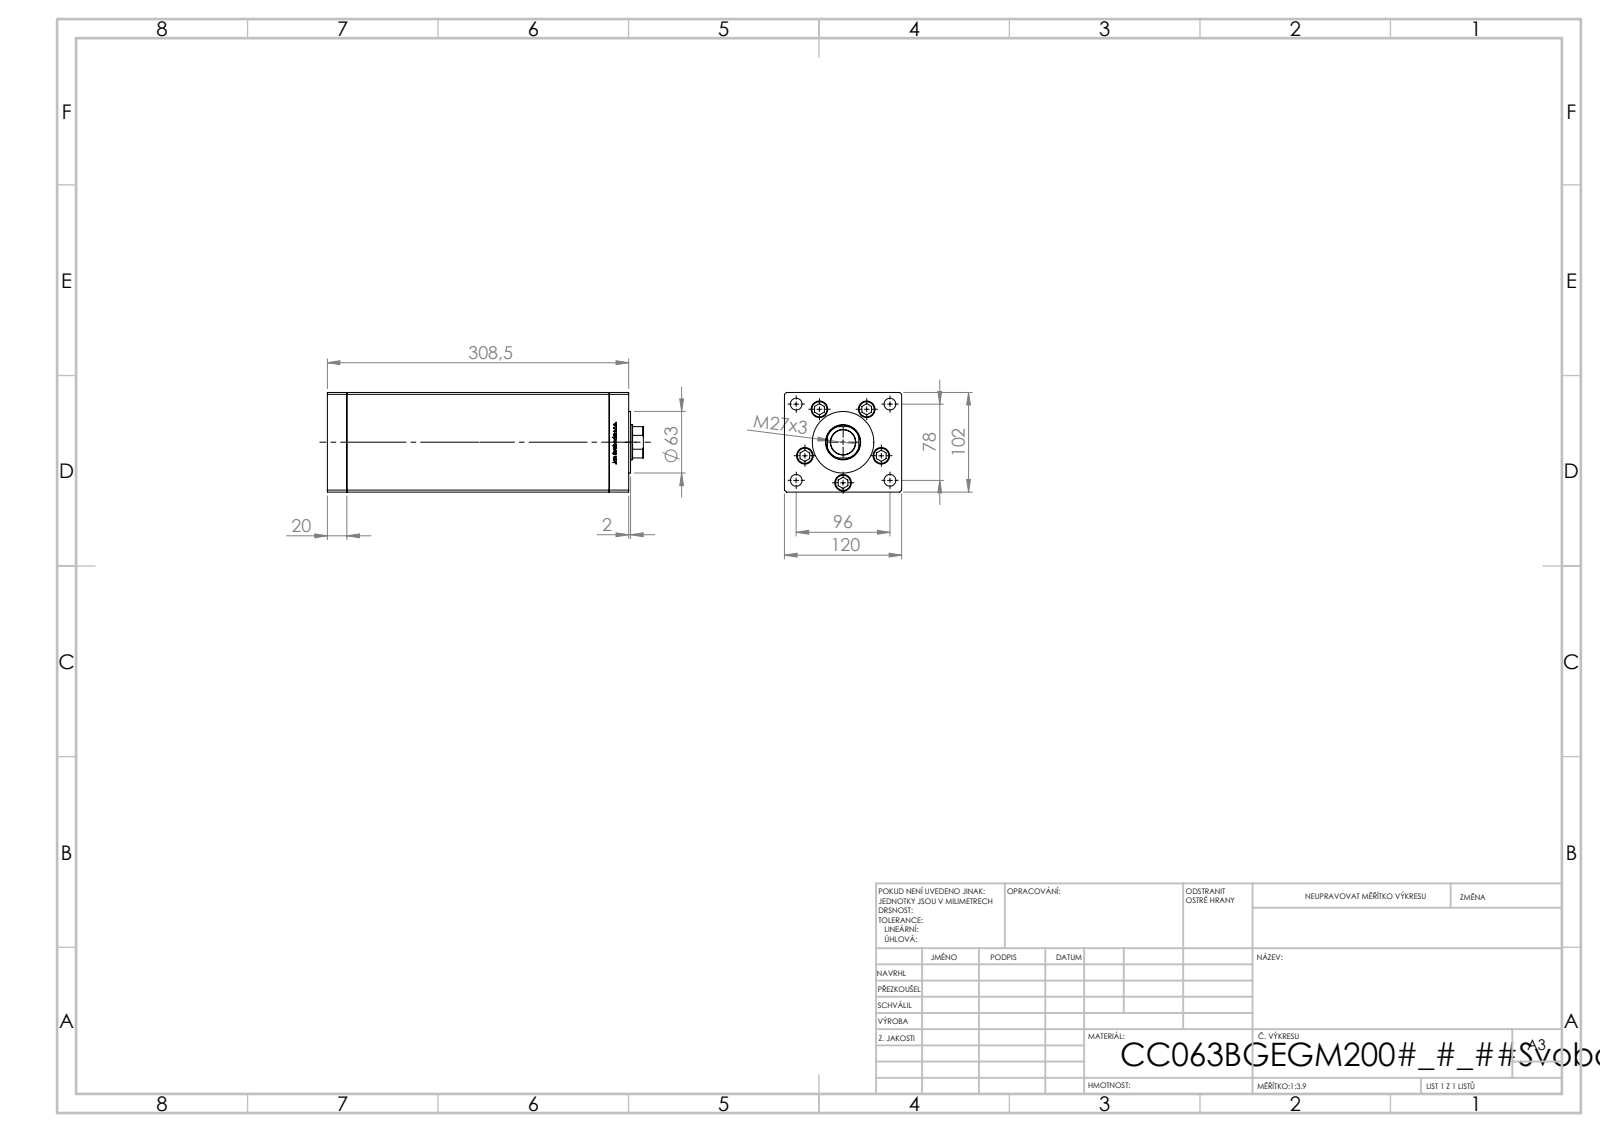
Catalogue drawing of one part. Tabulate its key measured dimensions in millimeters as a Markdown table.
| quantity | value |
| --- | --- |
| part name | V220C BACK_B; V220C_FRONT_B; V220C_B MIDDLE; ALLEN BOLT (+1 more) |
| STEP written by | SolidWorks 2019 (CONFIG_CONTROL_DESIGN) |
| units | millimeters |
| bodies | 14 solids, 1185 faces (464 planar, 147 cylindrical, 574 other) |
| overall size | 323.5 × 120 × 102 |
| volume | 3 241 000 mm³ |
| surface area | 348 914 mm² |
| round holes (diameter × count) | 13.5 × 5, 17 × 5, 12 × 4, 2 × 2, 13.16 × 2, 25.5 × 1, 36 × 1 |
| round bosses / shafts (diameter × count) | 8 × 5, 63 × 1 |
| partial cylindrical surfaces (radius × count) | 0.93 × 2, 17.5 × 1 |
| main face-to-face distances | 120, 102, 20, 268.5, 288.5, 34.25, 308.5, 14.25, 254.25, 274.25 |
| hole center spacings | 41.5, 61.85, 24.39, 26.69, 47.92, 48.07, 49.84, 53.57 |
